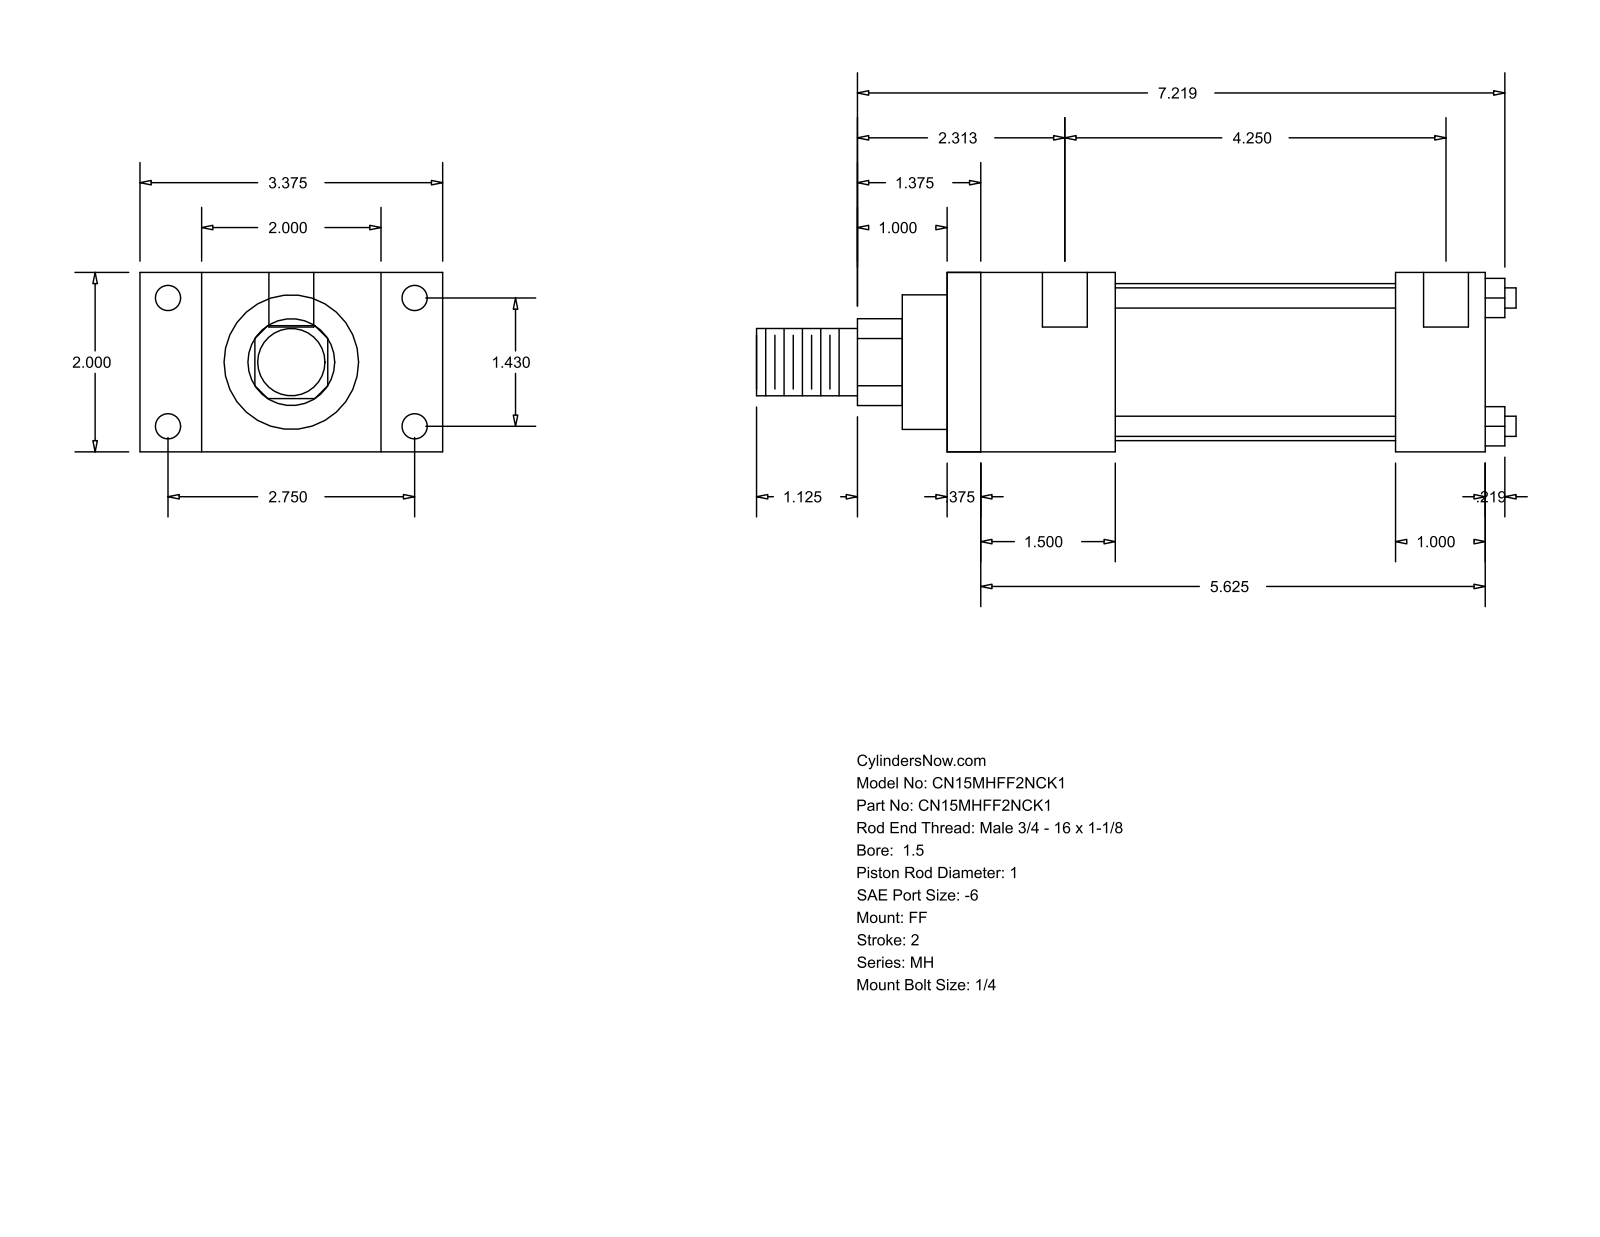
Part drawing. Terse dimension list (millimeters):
name: MH_FF__0150_1
written by: GSSL Pune (CONFIG_CONTROL_DESIGN)
unit: mm
bodies: 0 solids, 92 faces (64 planar, 28 cylindrical, 0 other)
size: 215.11 × 85.72 × 50.8
holes: 4× ⌀5.56, 4× ⌀7.14, 2× ⌀12.7
bosses: 4× ⌀5.71, 1× ⌀44.45, 1× ⌀38.1, 1× ⌀25.4, 1× ⌀19.05
rounds: 1× R12.29
face distances: 50.8, 152.4, 9.52, 142.88, 25.4, 17.46, 68.26, 47.63, 38.11, 104.77
hole spacings: 36.32, 69.84, 78.72, 111.13, 3.18, 107.95
